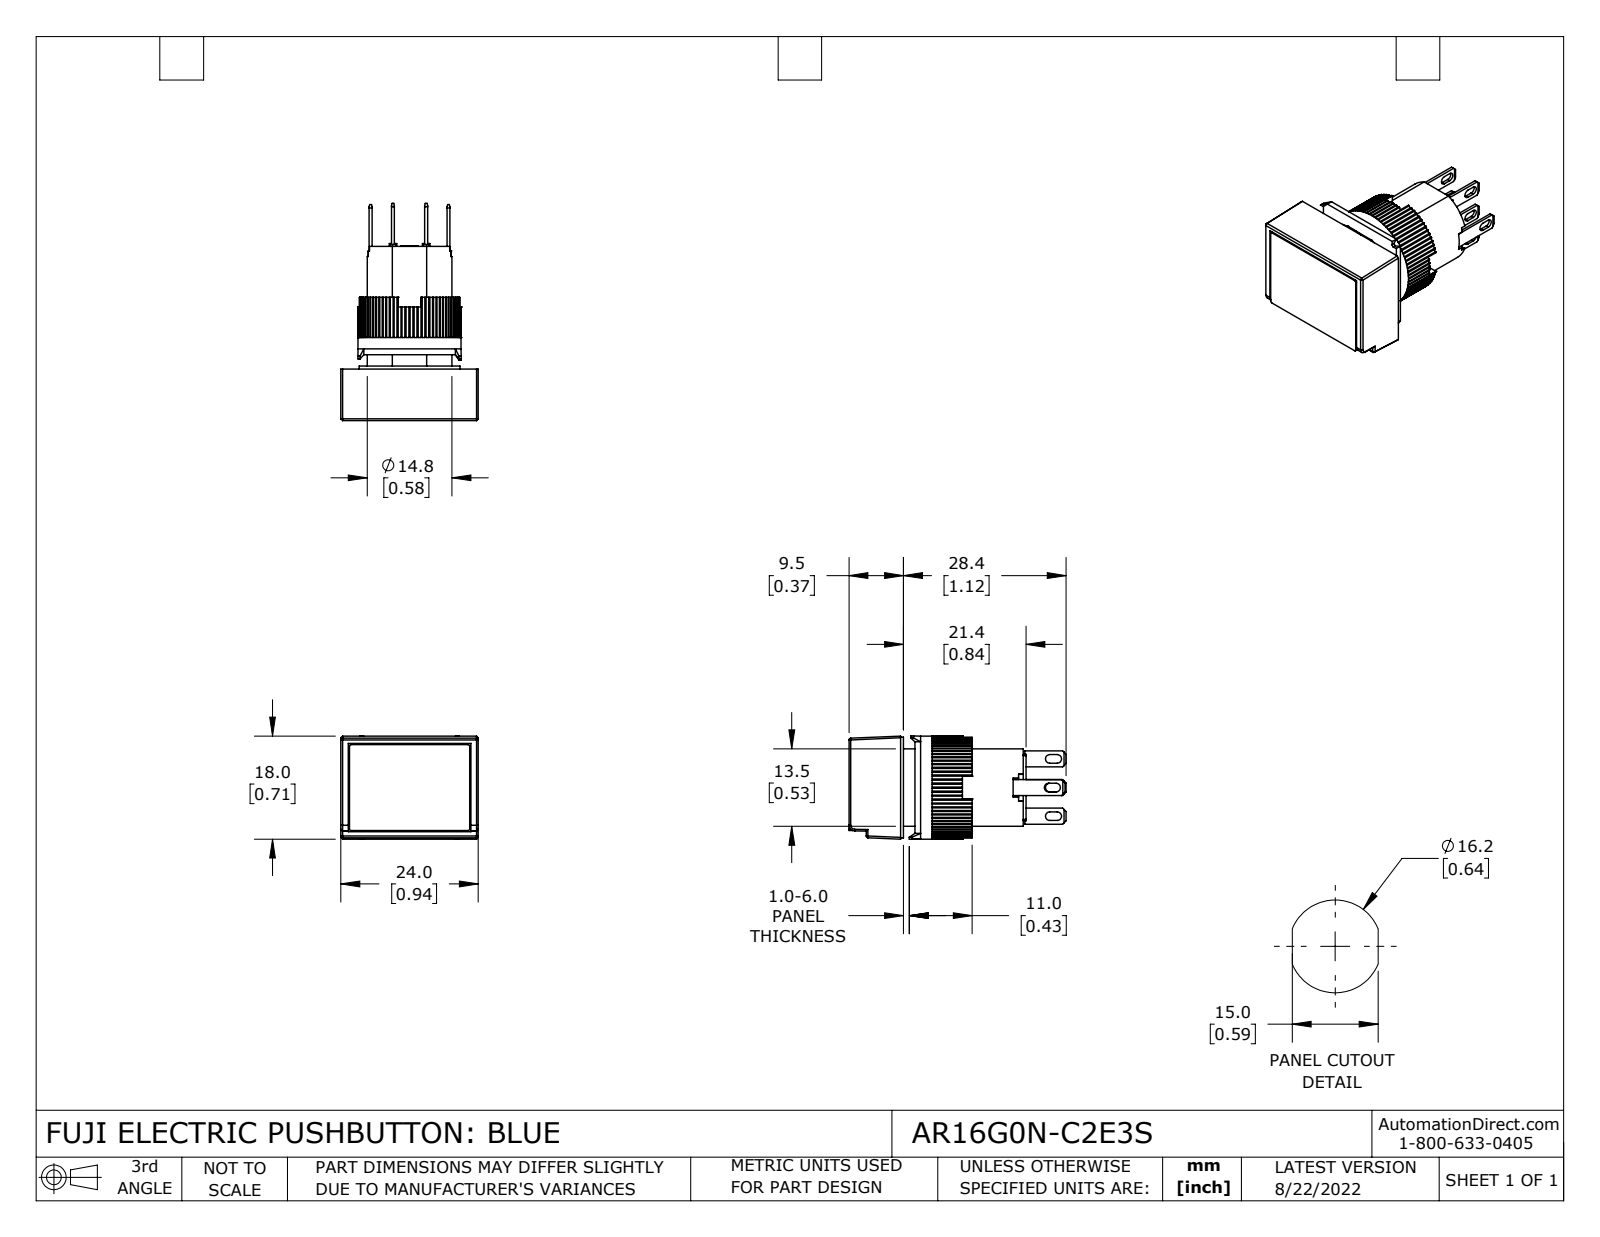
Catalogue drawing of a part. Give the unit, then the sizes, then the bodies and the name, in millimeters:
Units: millimetres
Overall size (bounding box): 37.9 × 24 × 18
Round holes (diameter × count): ⌀13.8 ×1, ⌀14.8 ×1
Round bosses / shafts (diameter × count): ⌀18 ×1, ⌀17.6 ×1
Partial cylindrical surfaces — rounded edges, fillets, slot ends (radius × count): R0.3 ×80, R0.2 ×12, R0.8 ×8, R0.3 ×6, R1 ×1
Main face-to-face distances: 5.4, 9, 3.6, 8.9, 12.5, 3.5, 0.5, 21.4, 1.5, 11.5
Volume: 7 340 mm³ · Surface area: 6 131 mm²
Bodies: 14 solids, 841 faces (654 planar, 181 cylindrical, 6 other)
Part name (STEP PRODUCT): AR16G0N-C2E3S
STEP written by: SolidWorks 2021 (CONFIG_CONTROL_DESIGN)
